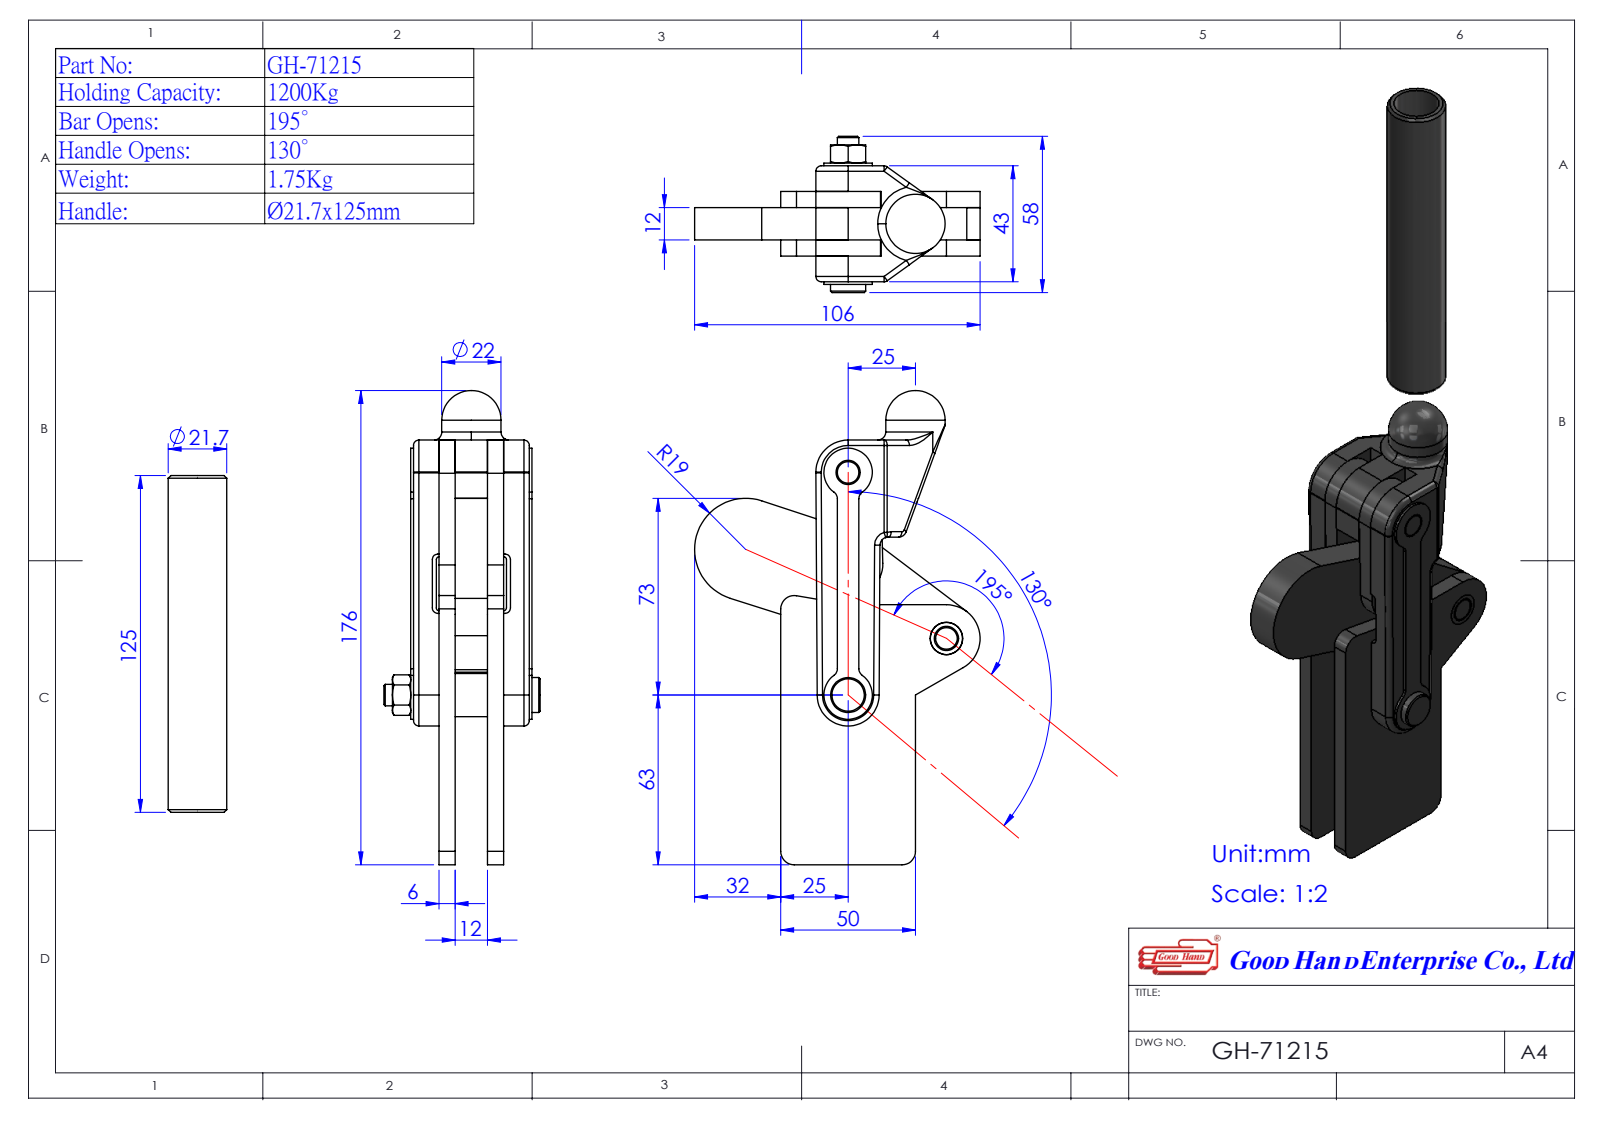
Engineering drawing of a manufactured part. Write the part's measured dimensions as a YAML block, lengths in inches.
part_name: "471210125-1^GH-71215(簡化)-1; GH-71215(簡化)-1; Group6^GH-71215(簡化)-1; Group1^GH-71215(簡化)-1 (+2 more)"
step_written_by: "SolidWorks 2016 (AUTOMOTIVE_DESIGN)"
units: inches
bodies: {solids: 5, faces: 197, planar: 71, cylindrical: 93, other: 33}
overall_size: [11.867, 4.176, 2.283]
volume: 13.82
surface_area: 124.5
round_holes:
  - {diameter: 0.315, count: 4}
  - {diameter: 0.634, count: 1}
round_bosses_or_shafts:
  - {diameter: 0.709, count: 2}
  - {diameter: 0.866, count: 1}
  - {diameter: 0.854, count: 1}
  - {diameter: 0.512, count: 1}
partial_cylinders:
  - {radius: 0.079, count: 14}
  - {radius: 0.118, count: 6}
  - {radius: 0.197, count: 3}
  - {radius: 0.472, count: 2}
  - {radius: 0.433, count: 1}
  - {radius: 0.453, count: 1}
  - {radius: 0.492, count: 1}
  - {radius: 0.751, count: 1}
face_to_face_distances: [0.236, 0.709, 0.472, 0.945, 0.242, 0.715, 0.951, 0.368, 0.374, 0.61]
hole_center_spacings: [1.339, 1.658, 1.773, 1.914, 2.819, 3.252]
